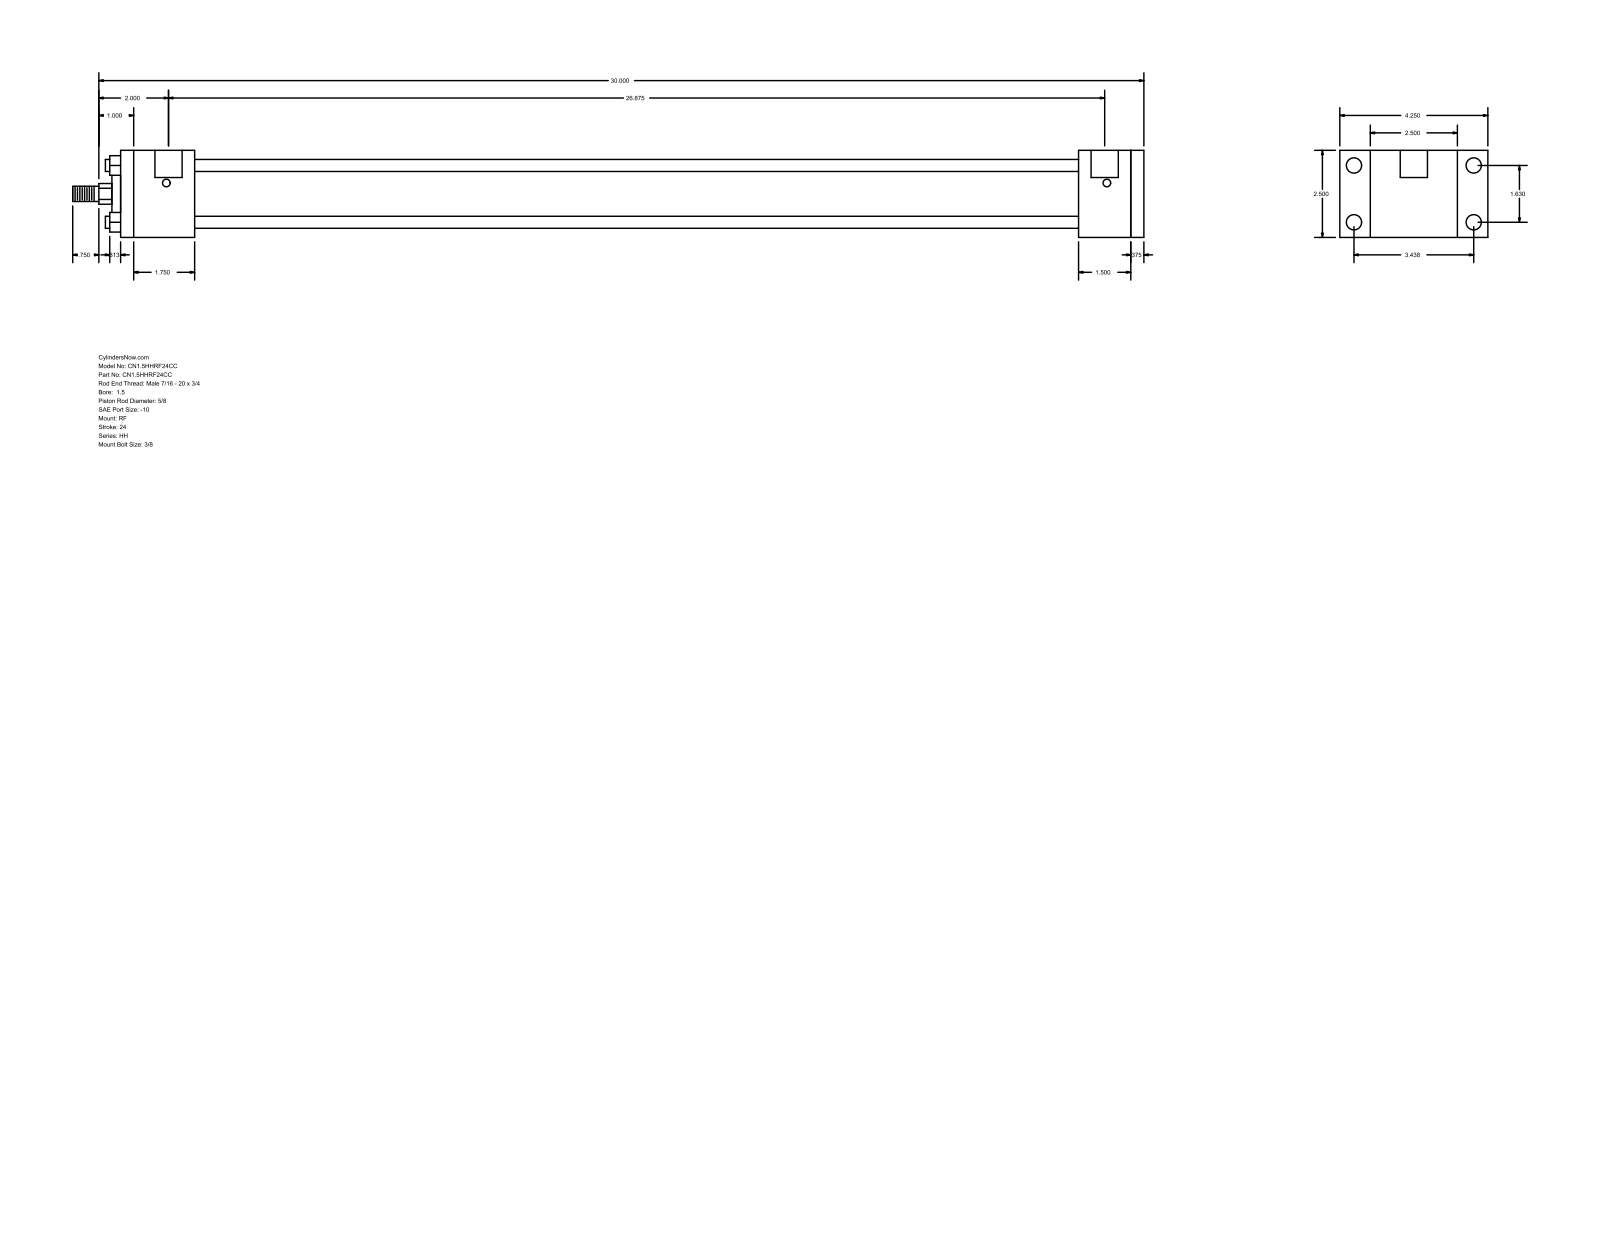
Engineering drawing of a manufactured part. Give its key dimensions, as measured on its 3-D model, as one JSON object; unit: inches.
{"part_name": "HH_RF__0150_0.625", "step_written_by": "GSSL Pune (CONFIG_CONTROL_DESIGN)", "units": "inches", "bodies": {"solids": 0, "faces": 92, "planar": 64, "cylindrical": 28, "other": 0}, "overall_size": [30.75, 4.25, 2.5], "round_holes": [[0.219, 4], [0.438, 4], [0.781, 2]], "round_bosses_or_shafts": [[0.345, 4], [1.75, 1], [1.125, 1], [0.625, 1], [0.437, 1]], "partial_cylinders_radius": [[0.297, 1]], "face_to_face_distances": [2.5, 29.375, 1.5, 29, 0.375, 2.125, 27.5, 25.375, 26.875, 27.25], "hole_center_spacings": [0.063, 1.63, 3.438, 3.805, 26.937, 27, 26.875]}
